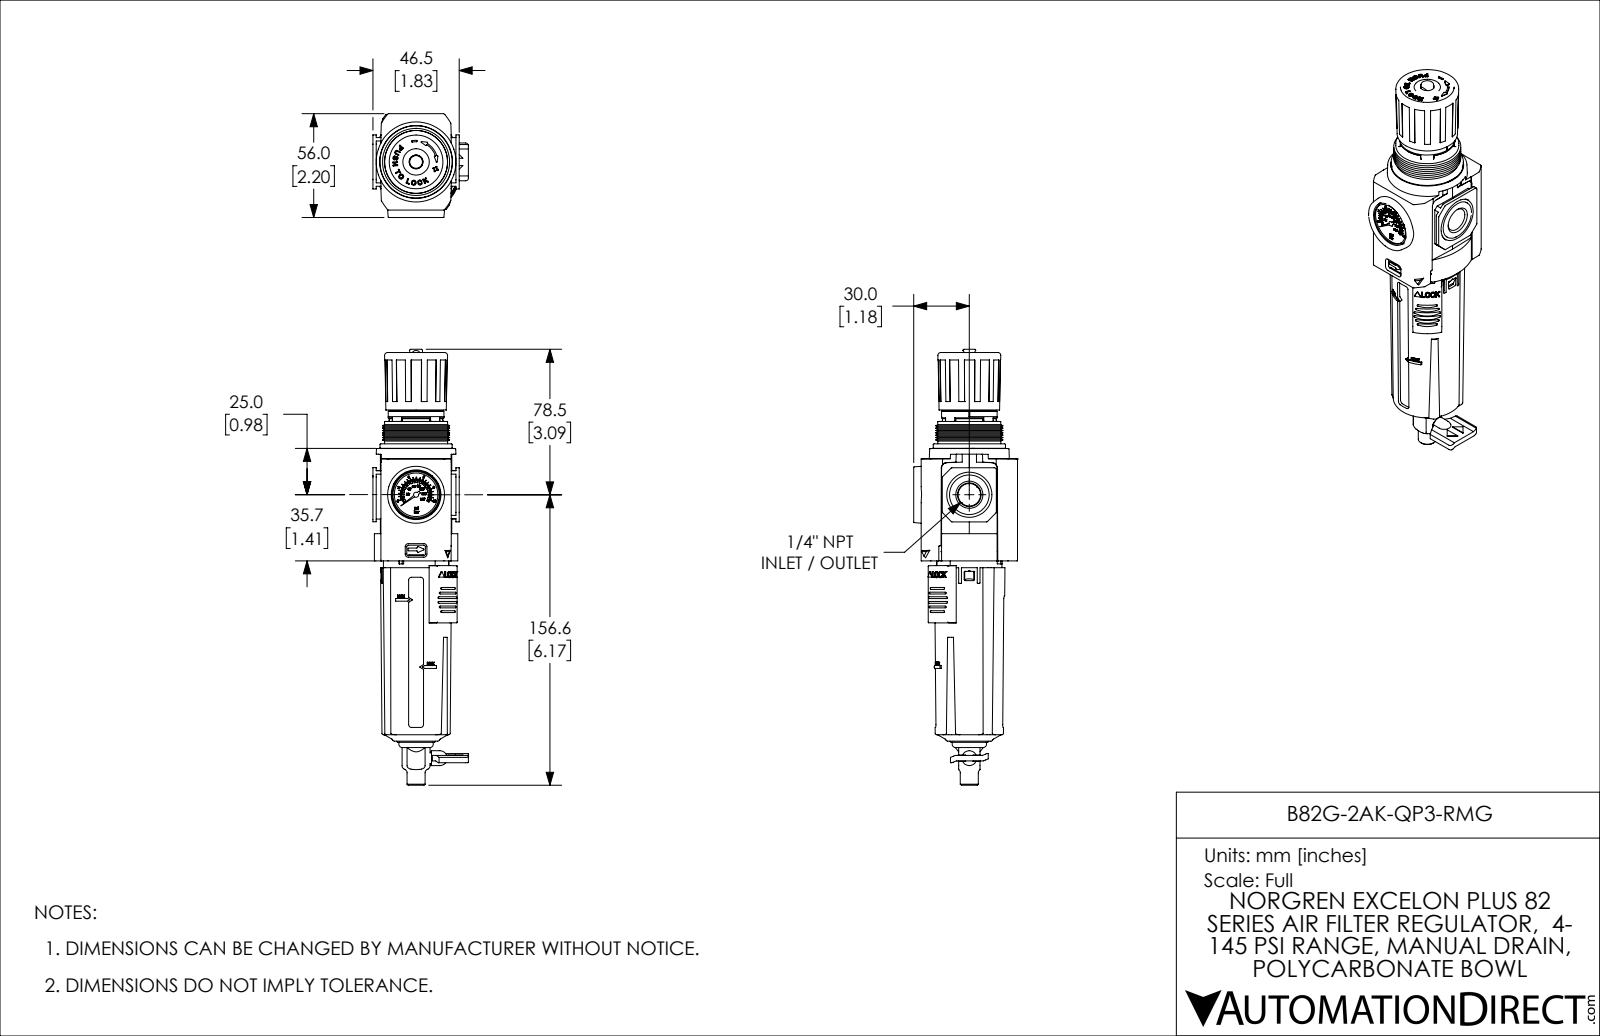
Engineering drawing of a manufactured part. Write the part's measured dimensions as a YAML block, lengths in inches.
part_name: "B82G-2AK-QP3-RMG"
step_written_by: "SolidWorks 2021 (CONFIG_CONTROL_DESIGN)"
units: inches
bodies: {solids: 8, faces: 2685, planar: 1044, cylindrical: 1230, other: 411}
overall_size: [9.257, 2.205, 2.027]
volume: 17.65
surface_area: 116
round_holes:
  - {diameter: 0.097, count: 4}
  - {diameter: 0.138, count: 2}
  - {diameter: 0.128, count: 1}
  - {diameter: 0.197, count: 1}
  - {diameter: 0.236, count: 1}
  - {diameter: 0.25, count: 1}
  - {diameter: 0.63, count: 1}
  - {diameter: 0.925, count: 1}
  - {diameter: 1.102, count: 1}
  - {diameter: 1.354, count: 1}
round_bosses_or_shafts:
  - {diameter: 0.224, count: 2}
  - {diameter: 0.118, count: 2}
  - {diameter: 1.535, count: 1}
  - {diameter: 1.388, count: 1}
  - {diameter: 1.356, count: 1}
  - {diameter: 1.339, count: 1}
  - {diameter: 1.291, count: 1}
  - {diameter: 1.257, count: 1}
partial_cylinders:
  - {radius: 0.02, count: 55}
  - {radius: 0.039, count: 30}
  - {radius: 0.009, count: 25}
  - {radius: 0.031, count: 20}
  - {radius: 0.006, count: 19}
  - {radius: 0.012, count: 15}
  - {radius: 0.012, count: 12}
  - {radius: 0.012, count: 12}
face_to_face_distances: [0.059, 1.988, 1.693, 0.354, 1.634, 0.295, 1.417, 1.475, 0.236, 0.182]
hole_center_spacings: [0.63, 1.091, 1.26, 2.705, 3.325, 2.965]
